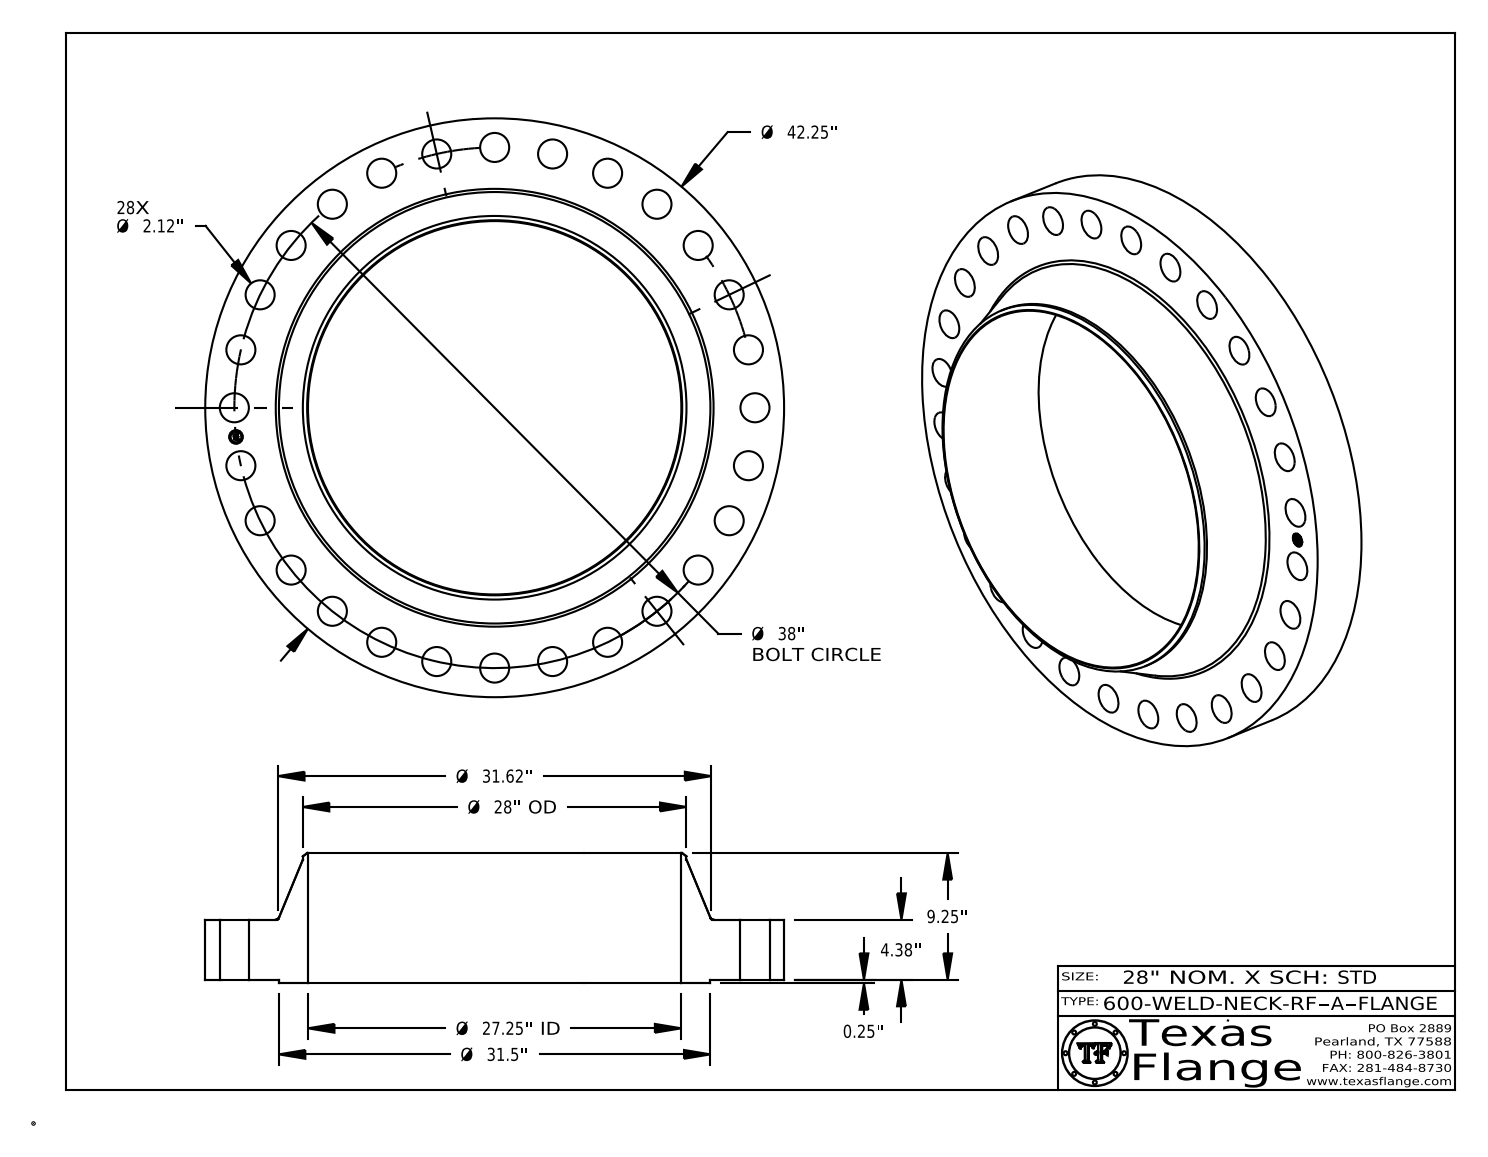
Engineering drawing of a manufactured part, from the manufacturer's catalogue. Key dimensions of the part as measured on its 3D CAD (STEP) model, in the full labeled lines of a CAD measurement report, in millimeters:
Part name (STEP PRODUCT): 600-WELD-NECK-RF, Series A
STEP written by: CATIA V5 STEP AP214 (AUTOMOTIVE_DESIGN)
Units: millimetres
Bodies: 1 solid, 459 faces (369 planar, 84 cylindrical, 6 other)
Overall size (bounding box): 1073.2 × 1073.2 × 241.3
Volume: 61 010 000 mm³ · Surface area: 2 565 000 mm²
Round holes (diameter × count): ⌀53.8 ×28, ⌀25.4 ×1, ⌀692.2 ×1
Round bosses / shafts (diameter × count): ⌀1.5 ×8, ⌀1073.2 ×1, ⌀800.1 ×1, ⌀711.2 ×1, ⌀20 ×1
Main face-to-face distances: 111.3, 6.4, 117.6, 241.3, 235, 123.7, 117.2, 110.9, 0.4, 124.1
Hole centre spacings: 482.6, 513.5, 682.5, 817.3, 911, 941, 959.1, 214.8
